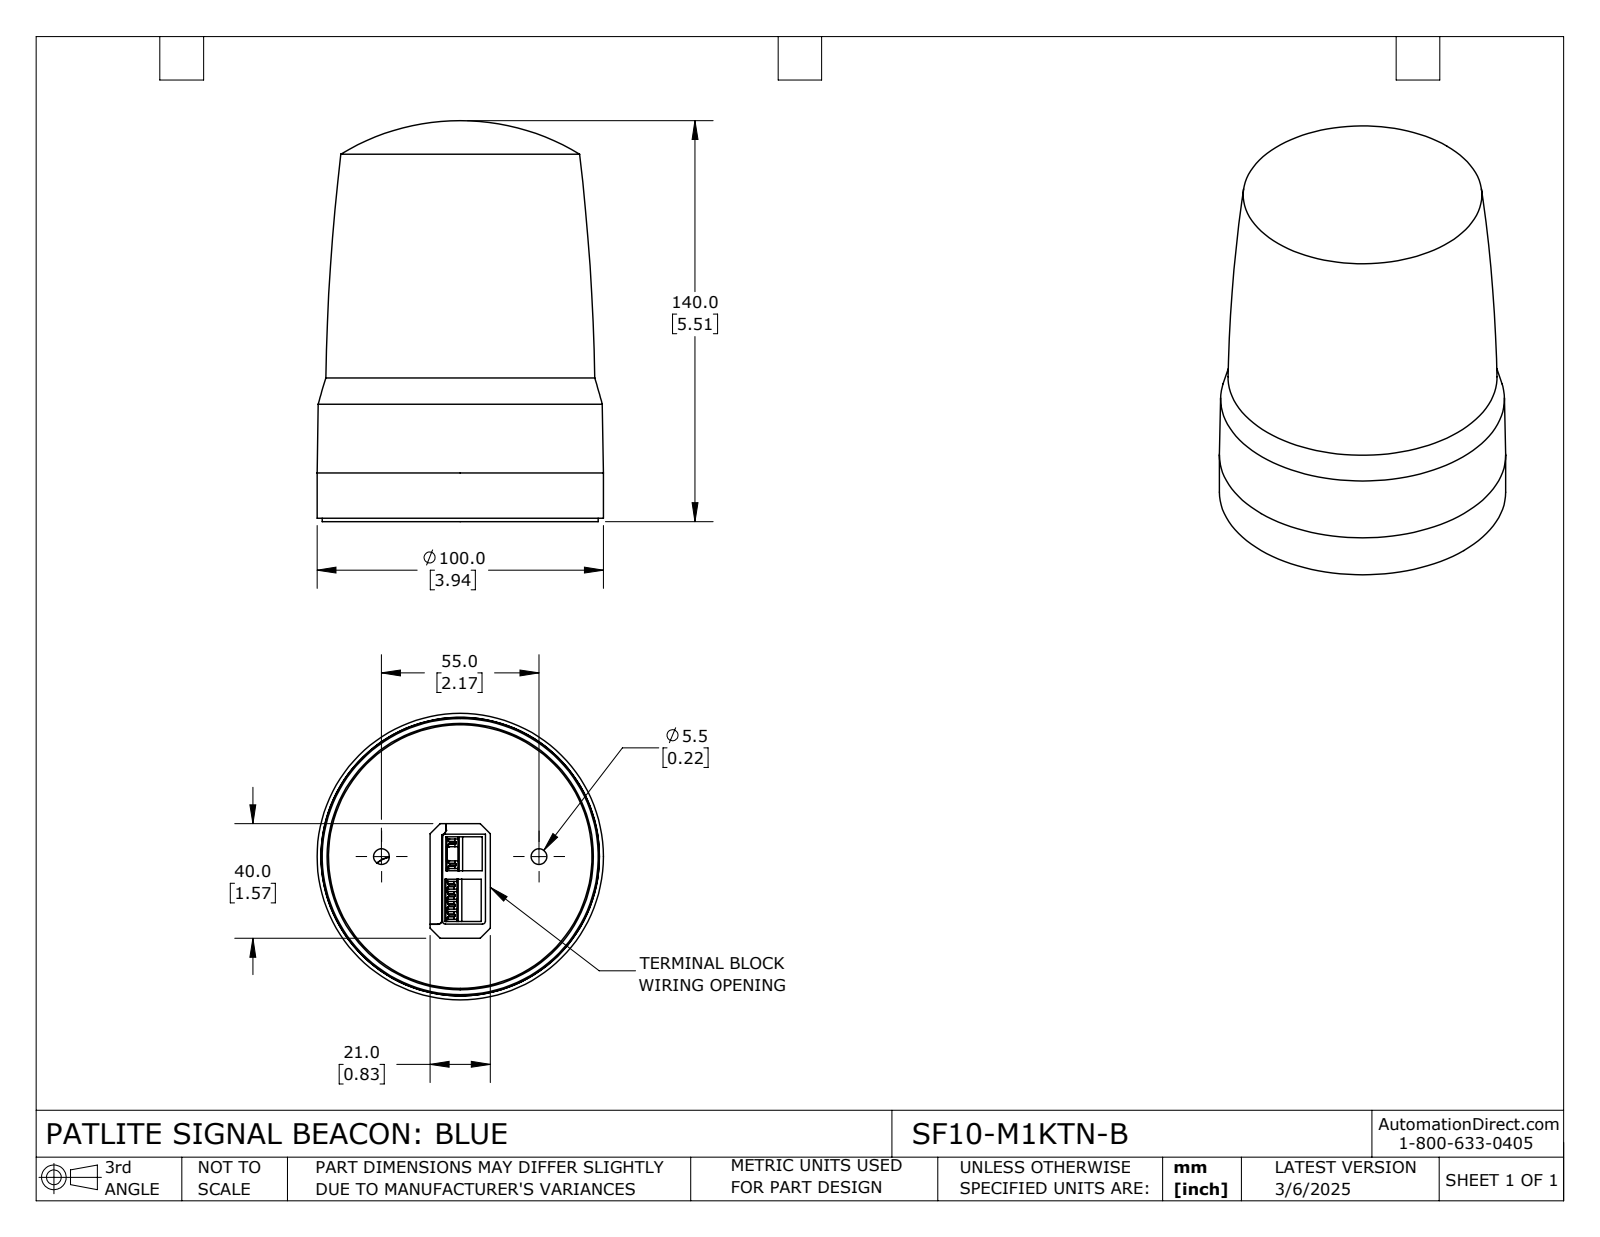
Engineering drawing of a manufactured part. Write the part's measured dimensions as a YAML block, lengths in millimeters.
part_name: "SF10-M1KTN-B"
step_written_by: "SolidWorks 2024 (CONFIG_CONTROL_DESIGN)"
units: millimeters
bodies: {solids: 2, faces: 268, planar: 183, cylindrical: 29, other: 56}
overall_size: [140, 100, 100]
volume: 857676
surface_area: 76986
round_holes:
  - {diameter: 5.5, count: 2}
  - {diameter: 13, count: 2}
  - {diameter: 93, count: 1}
  - {diameter: 95.6, count: 1}
round_bosses_or_shafts:
  - {diameter: 100, count: 1}
  - {diameter: 96.4, count: 1}
  - {diameter: 94.5, count: 1}
  - {diameter: 93.2, count: 1}
  - {diameter: 92, count: 1}
partial_cylinders:
  - {radius: 0.3, count: 2}
  - {radius: 44.32, count: 1}
  - {radius: 44.75, count: 1}
face_to_face_distances: [6.3, 14.7, 8.4, 1.5, 6.9, 13.2, 12.6, 3.15, 4.4, 7]
hole_center_spacings: [27.5, 55]
